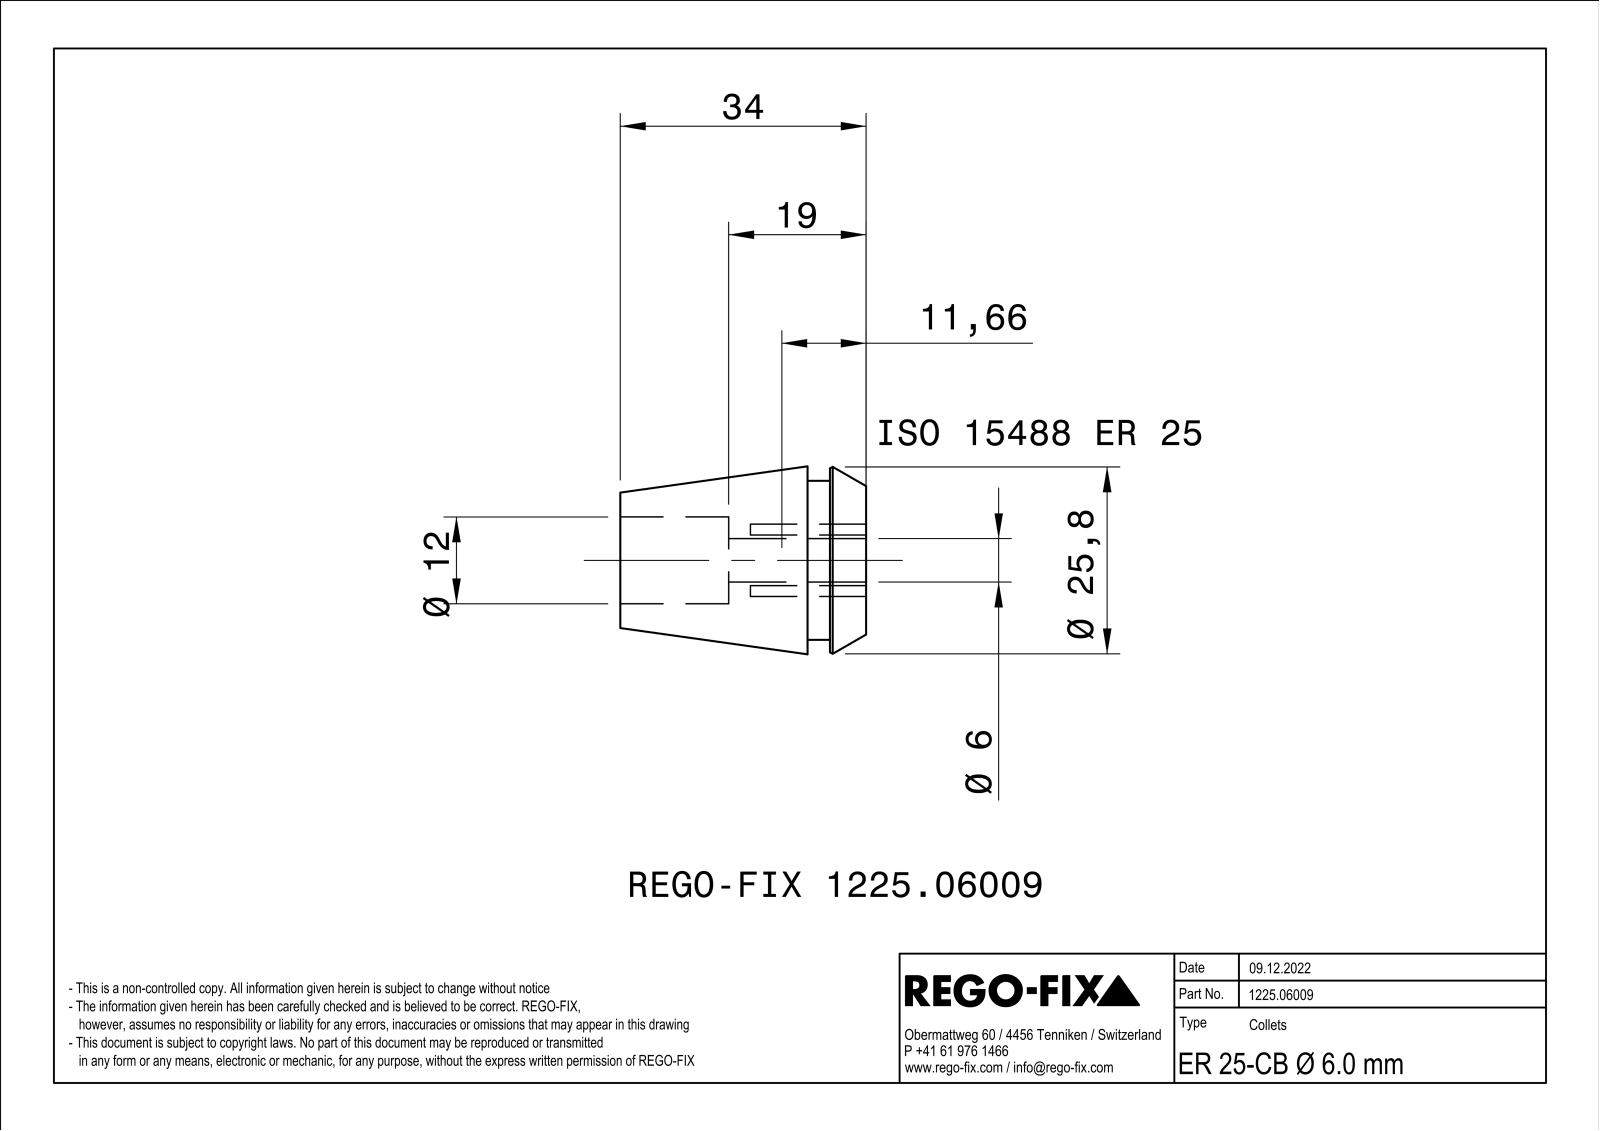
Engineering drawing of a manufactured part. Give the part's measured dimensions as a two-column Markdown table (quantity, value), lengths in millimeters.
| quantity | value |
| --- | --- |
| part name | NOCUT |
| STEP written by | SIEMENS PLM Software Solid Edge ST10 (AUTOMOTIVE_DESIGN) |
| units | millimeters |
| bodies | 1 solid, 114 faces (36 planar, 17 cylindrical, 61 other) |
| overall size | 34 × 25.87 × 25.87 |
| volume | 10 911 mm³ |
| surface area | 6 644 mm² |
| round holes (diameter × count) | 1.5 × 4, 6 × 1, 12 × 1 |
| round bosses / shafts (diameter × count) | 25.74 × 1, 22 × 1 |
| main face-to-face distances | 0.6, 5, 34, 29, 8.1, 3.1, 25.9, 24, 19, 15.9 |
| hole center spacings | 4.26, 6.02, 8.51 |
